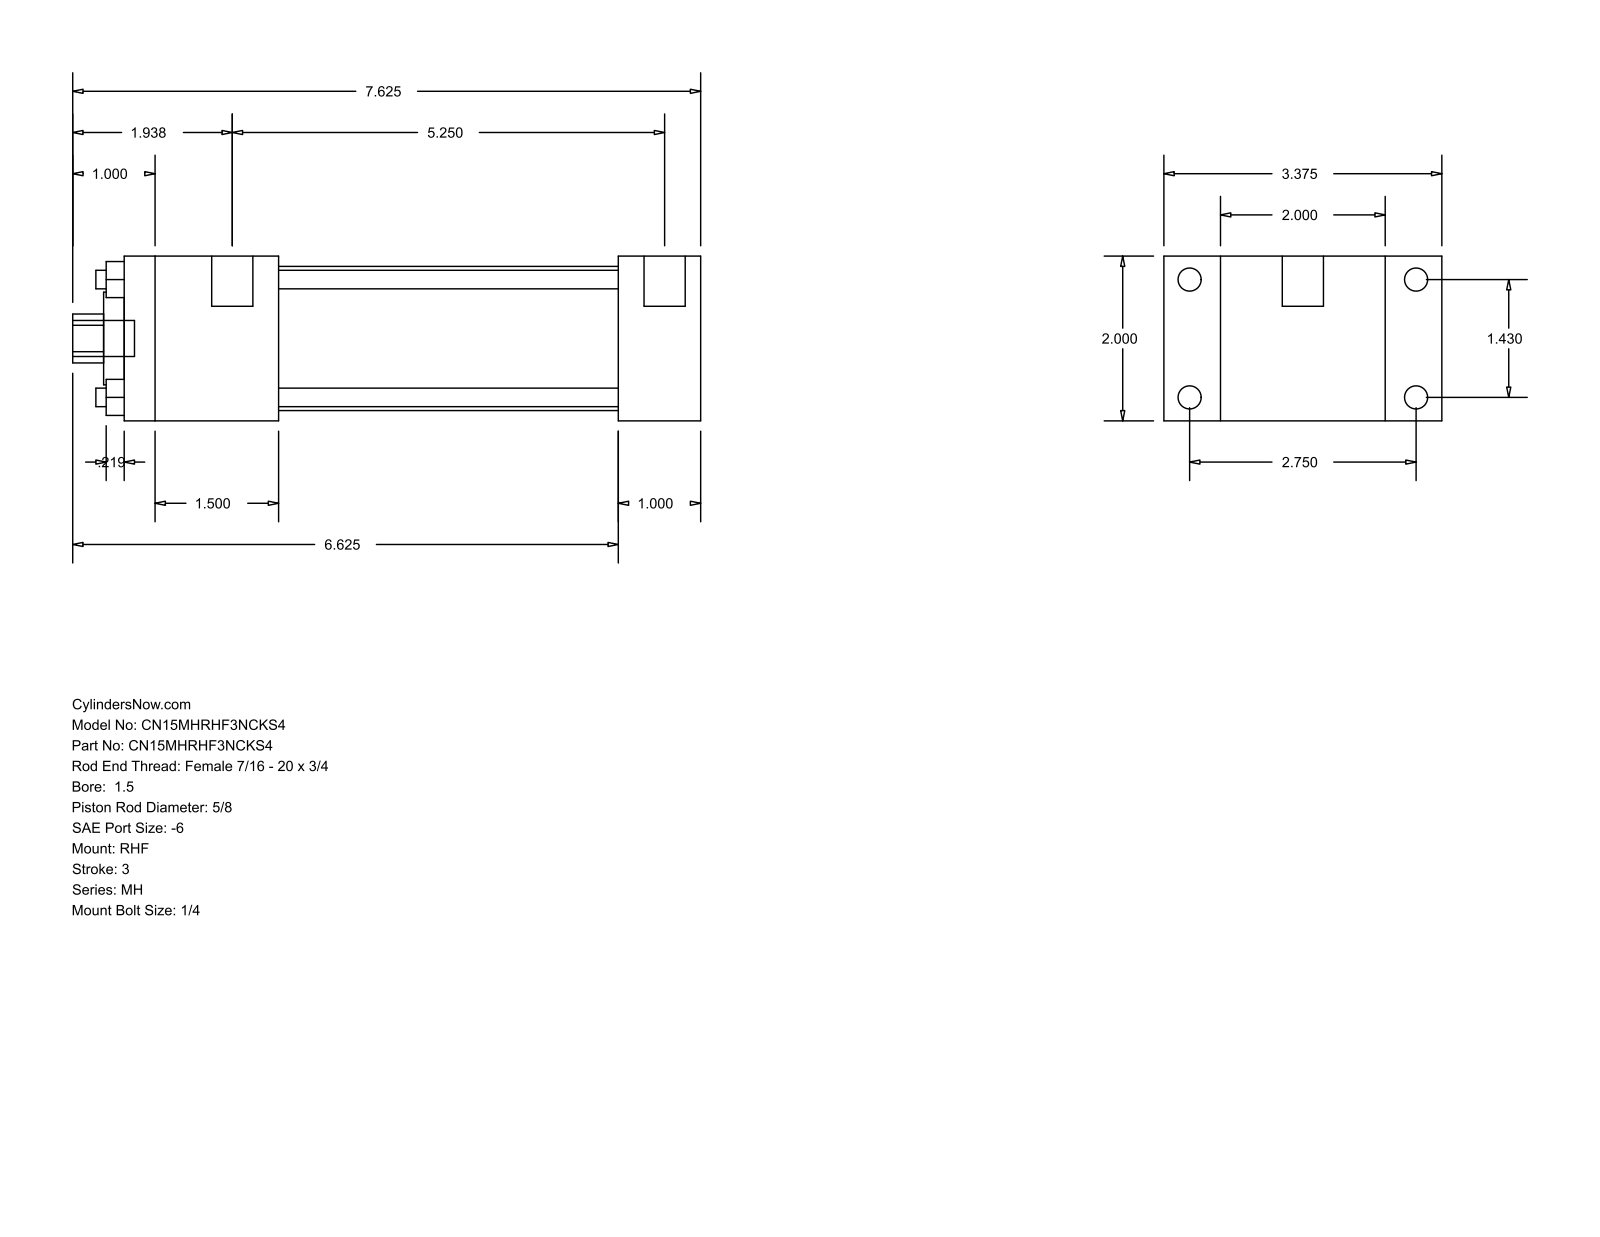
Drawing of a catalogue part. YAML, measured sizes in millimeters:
part_name: "MH_RHF__0150_0.625"
step_written_by: "GSSL Pune (CONFIG_CONTROL_DESIGN)"
units: millimeters
bodies: {solids: 0, faces: 88, planar: 60, cylindrical: 28, other: 0}
overall_size: [193.68, 85.72, 50.8]
round_holes:
  - {diameter: 5.71, count: 4}
  - {diameter: 15.88, count: 1}
  - {diameter: 28.57, count: 1}
  - {diameter: 44.45, count: 1}
round_bosses_or_shafts:
  - {diameter: 7.14, count: 4}
  - {diameter: 5.56, count: 4}
  - {diameter: 12.7, count: 2}
  - {diameter: 11.11, count: 1}
partial_cylinders:
  - {radius: 7.54, count: 1}
face_to_face_distances: [50.8, 17.46, 68.26, 25.4, 152.4, 177.8, 85.72, 47.62, 104.78, 130.18]
hole_center_spacings: [25.68, 36.32, 51.36]
